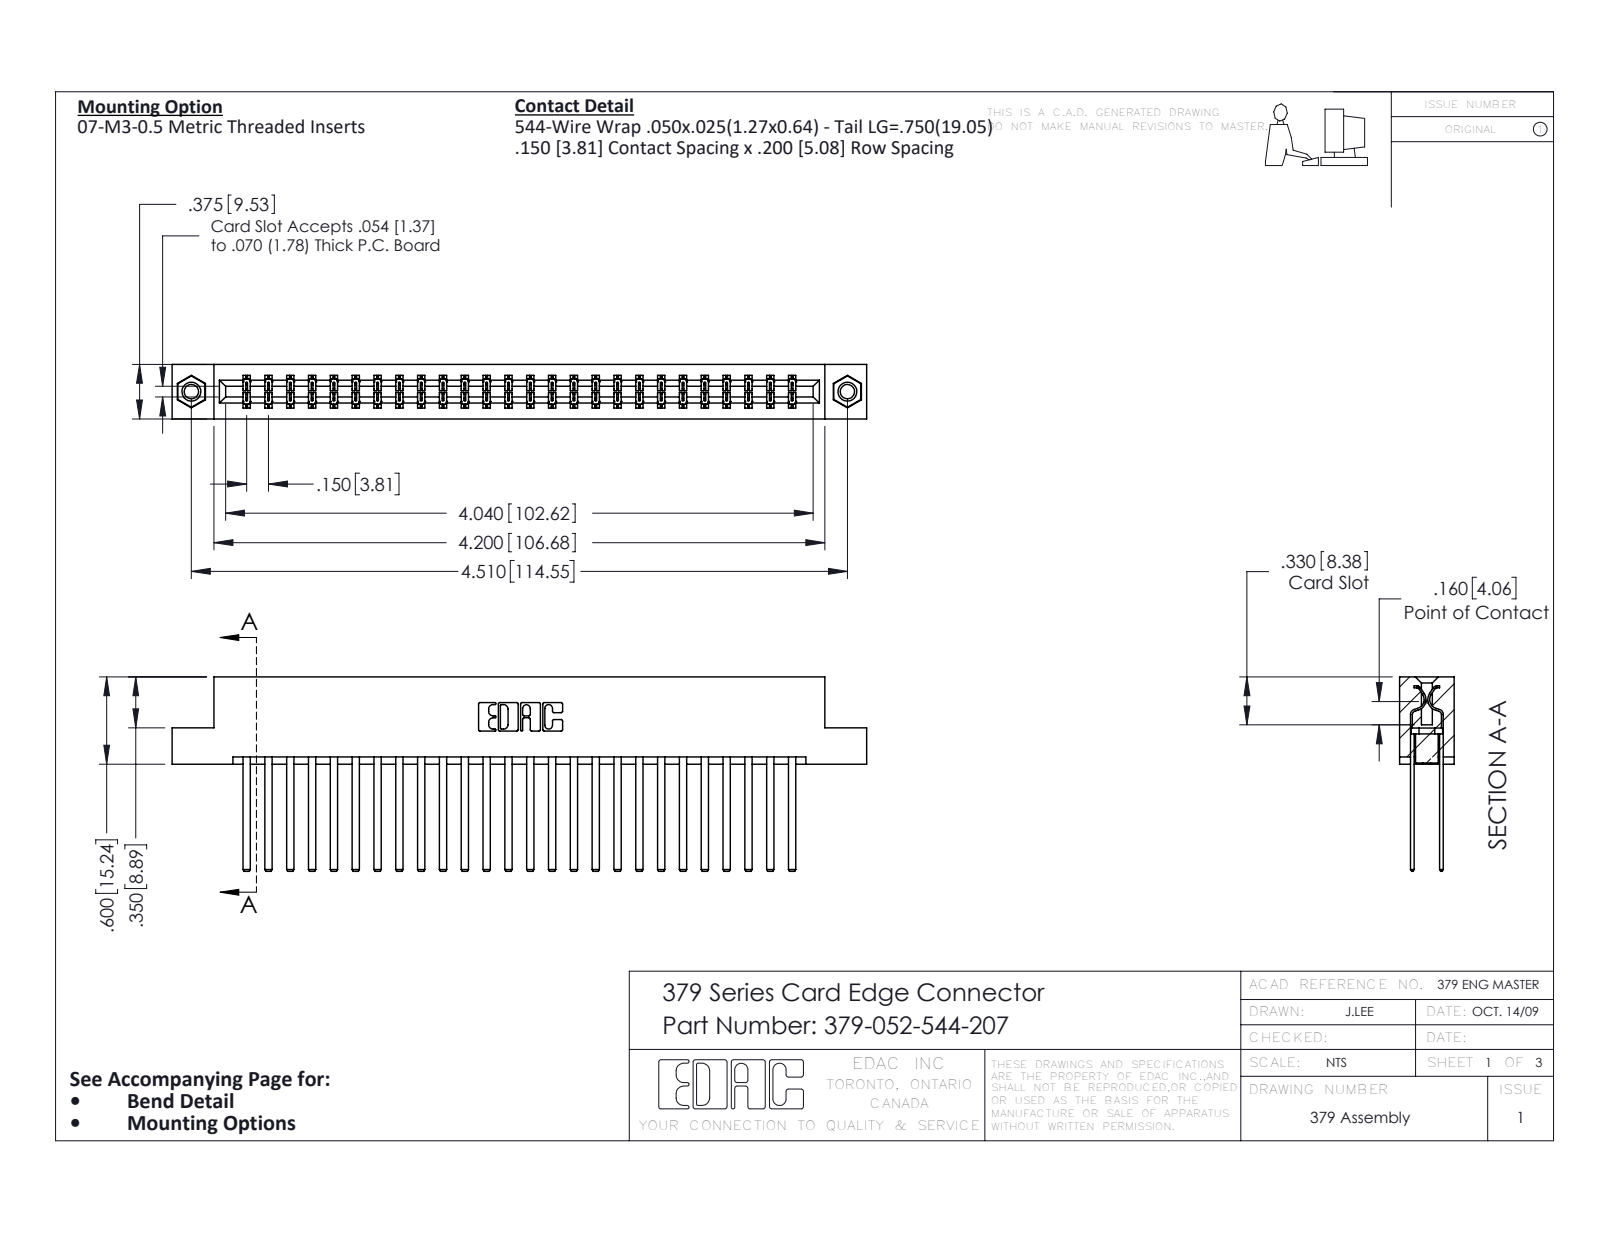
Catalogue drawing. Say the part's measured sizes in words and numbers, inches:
The part is named "345-292-001_345-293-144; 345-250-001_345-250-005-103; 379-052-544-207; 379 Part_Flush - .156 Dia - TI". Its 3-D file was written by "SolidWorks 2016 (CONFIG_CONTROL_DESIGN)". It is 55 solids with 2566 faces: 1766 planar, 784 cylindrical and 16 other. Overall it measures 4.775 by 1.337 by 0.375 inches. Its volume is 0.82 cubic inches and its surface area 26.92 square inches. Round holes: 2 of diameter 0.098, 2 of diameter 0.125, 2 of diameter 0.156. Round bosses or shafts: 2 of diameter 0.155. Partial cylindrical surfaces (rounded edges, fillets, slot ends): 78 of radius 0.006, 22 of radius 0.01, 6 of radius 0.007, 6 of radius 0.031, 3 of radius 0.026, 2 of radius 0.014, 2 of radius 0.022, 2 of radius 0.024. The main face-to-face distances are 0.3, 0.1, 0.075, 0.2, 0.275, 0.375, 0.025, 0.15, 0.6, 0.076. The hole center spacings are 4.51.
